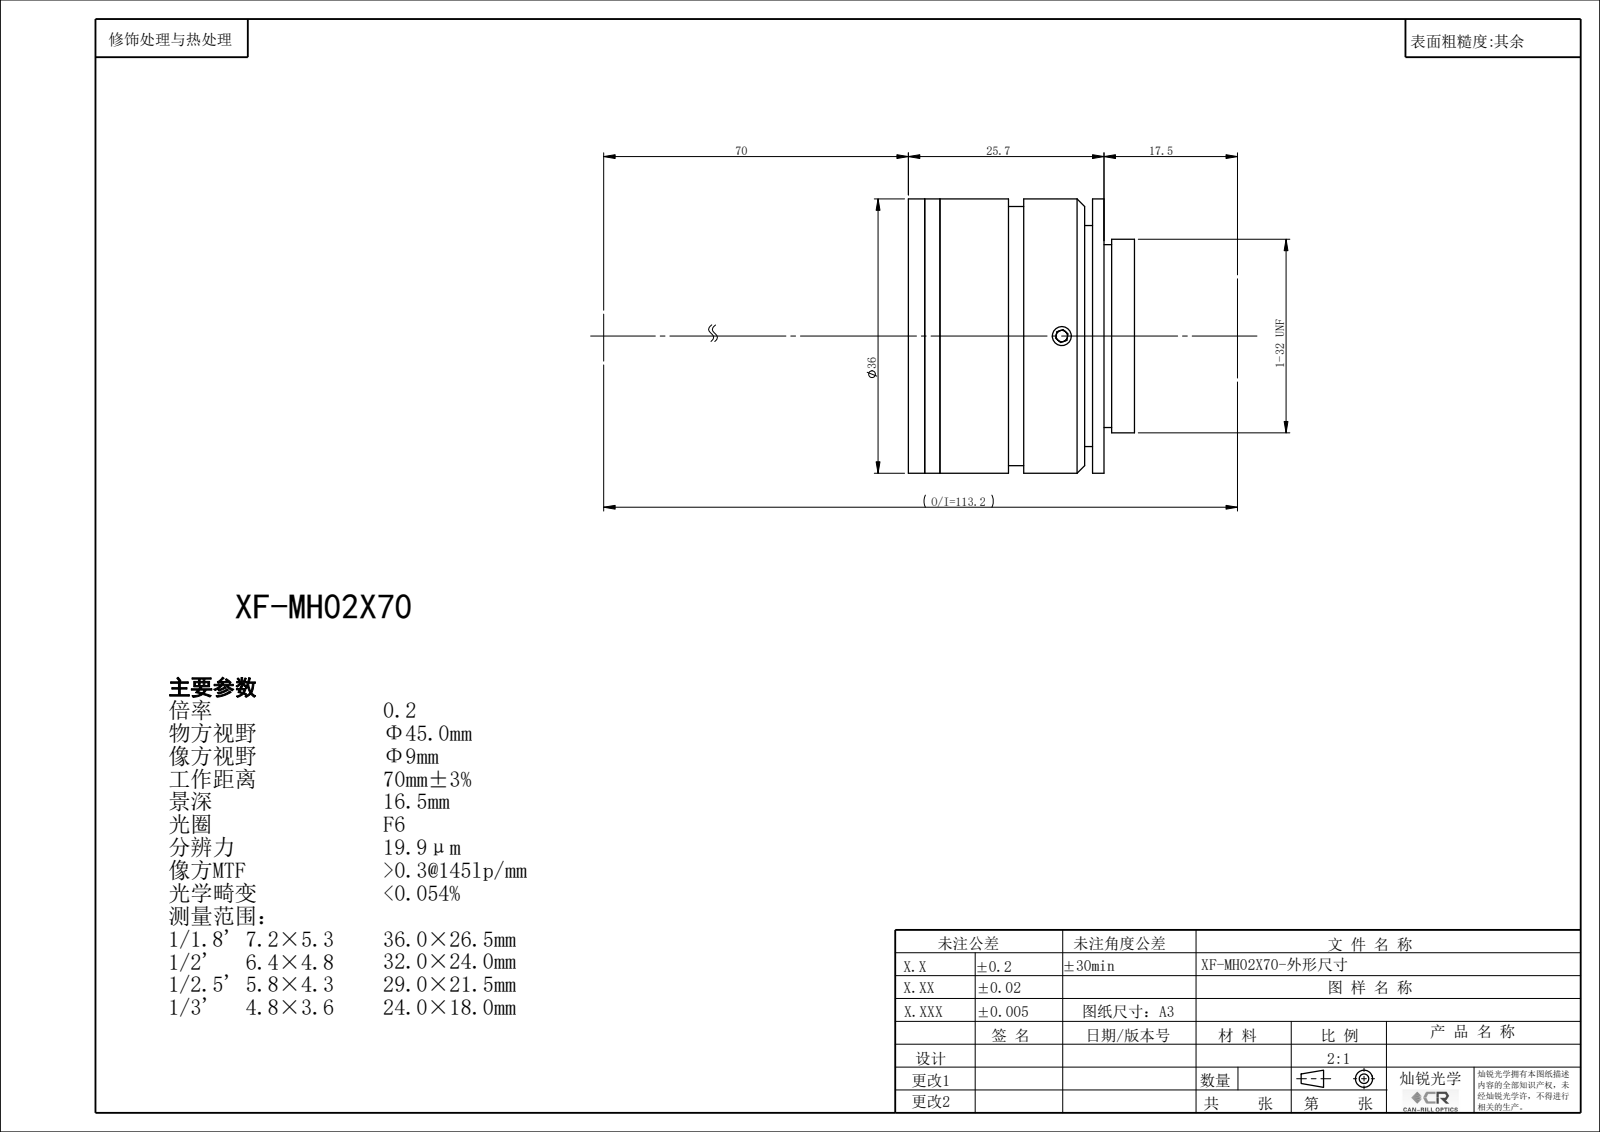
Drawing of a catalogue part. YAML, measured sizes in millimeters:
part_name: "XF-MH02X70"
step_written_by: "SolidWorks 2022 (CONFIG_CONTROL_DESIGN)"
units: millimeters
bodies: {solids: 0, faces: 109, planar: 51, cylindrical: 48, other: 10}
overall_size: [36, 36, 29.69]
round_holes:
  - {diameter: 2.5, count: 3}
  - {diameter: 7, count: 1}
  - {diameter: 8.4, count: 1}
  - {diameter: 10, count: 1}
  - {diameter: 12, count: 1}
  - {diameter: 14, count: 1}
  - {diameter: 16, count: 1}
  - {diameter: 18, count: 1}
  - {diameter: 20, count: 1}
  - {diameter: 21.5, count: 1}
  - {diameter: 22, count: 1}
  - {diameter: 24, count: 1}
round_bosses_or_shafts:
  - {diameter: 36, count: 1}
  - {diameter: 34, count: 1}
  - {diameter: 25.4, count: 1}
face_to_face_distances: [2, 4.15, 2.15, 23.54, 21.54, 25.69, 1, 1.5, 24.19, 22.04]
